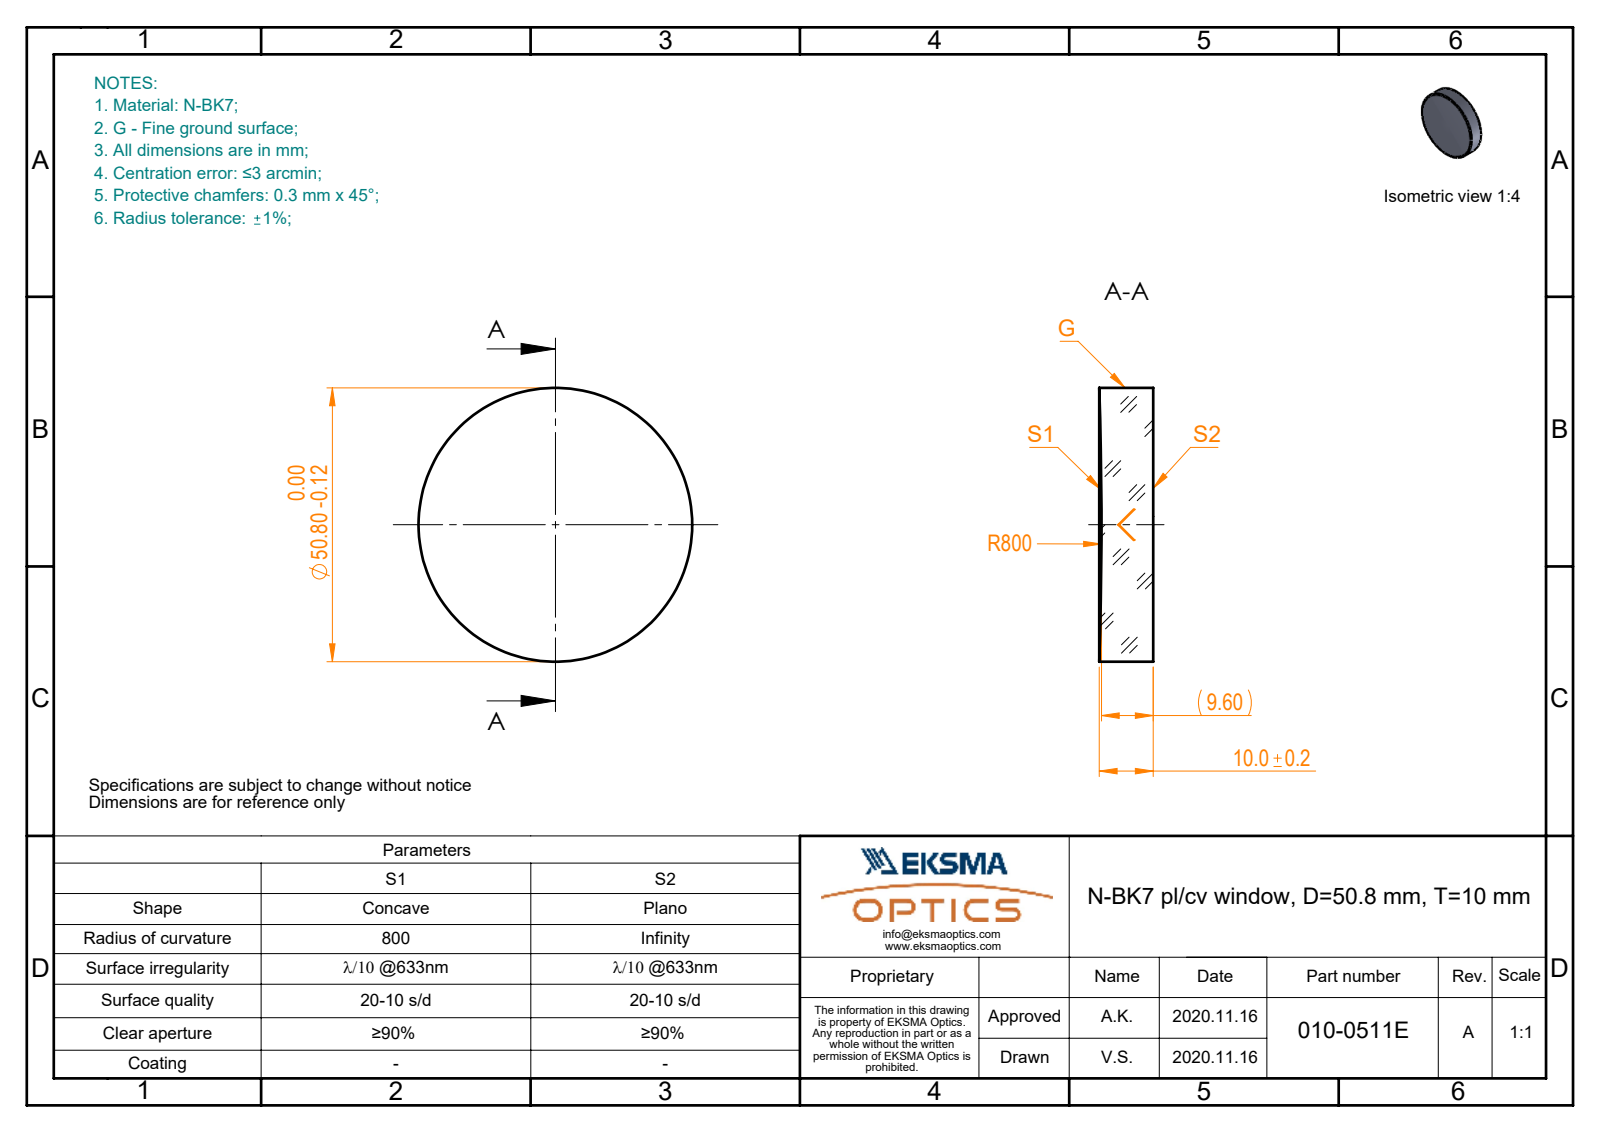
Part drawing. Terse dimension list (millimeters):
name: 010-0511E_N-BK7_PCV_window
written by: SolidWorks 2019 (CONFIG_CONTROL_DESIGN)
unit: mm
bodies: 1 solid, 5 faces (1 planar, 2 cylindrical, 2 other)
size: 50.8 × 50.8 × 10
volume: 19 860 mm³; area: 5 650 mm²
bosses: 1× ⌀50.8
